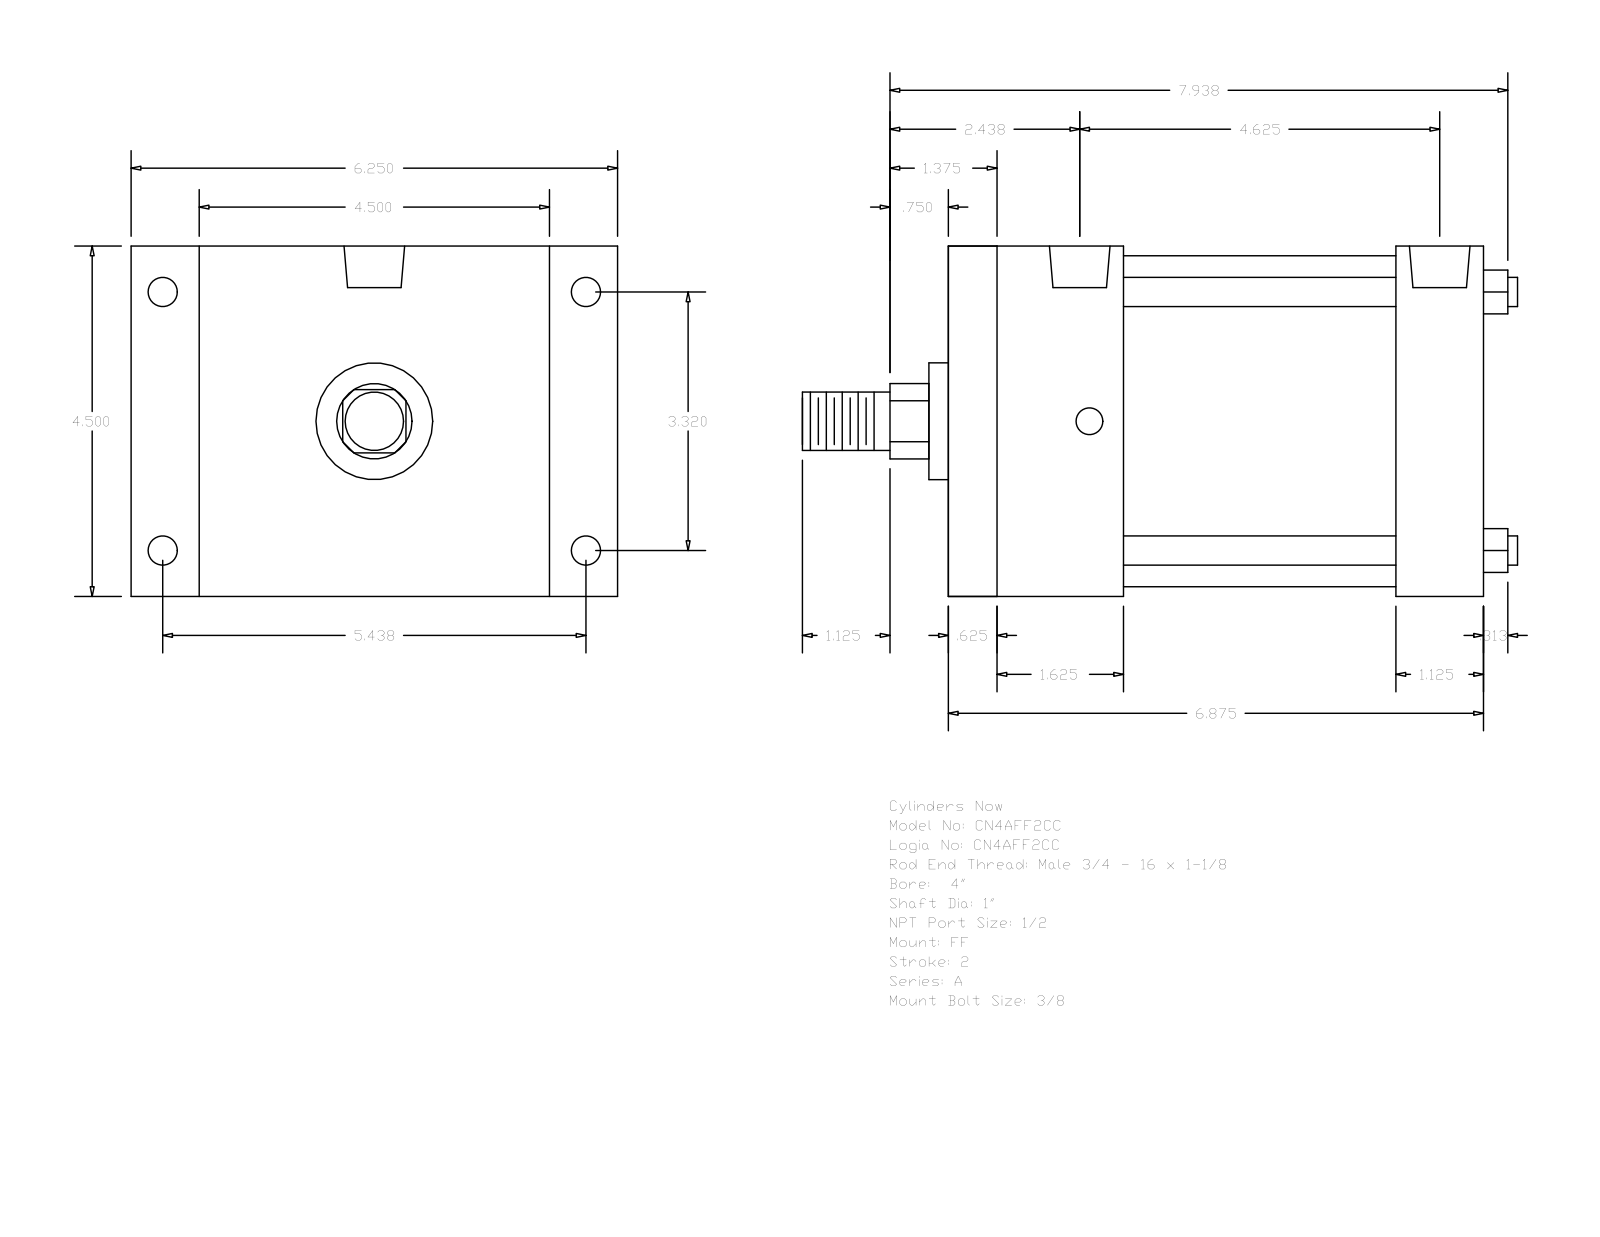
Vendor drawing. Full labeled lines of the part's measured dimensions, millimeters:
Part name (STEP PRODUCT): A_FF__0400_1
STEP written by: GSSL Pune (CONFIG_CONTROL_DESIGN)
Units: millimetres
Bodies: 0 solids, 92 faces (64 planar, 28 cylindrical, 0 other)
Overall size (bounding box): 233.36 × 158.75 × 114.3
Round holes (diameter × count): ⌀8.73 ×4, ⌀9.53 ×4, ⌀19.77 ×2
Round bosses / shafts (diameter × count): ⌀9.53 ×4, ⌀107.95 ×1, ⌀38.1 ×1, ⌀25.4 ×1, ⌀19.05 ×1
Partial cylindrical surfaces — rounded edges, fillets, slot ends (radius × count): R12.29 ×1
Main face-to-face distances: 114.3, 174.63, 158.76, 15.87, 22.23, 136.53, 146.05, 130.18, 28.58, 57.15
Hole centre spacings: 3.18, 84.32, 111.12, 114.3, 138.12, 161.82, 117.48
